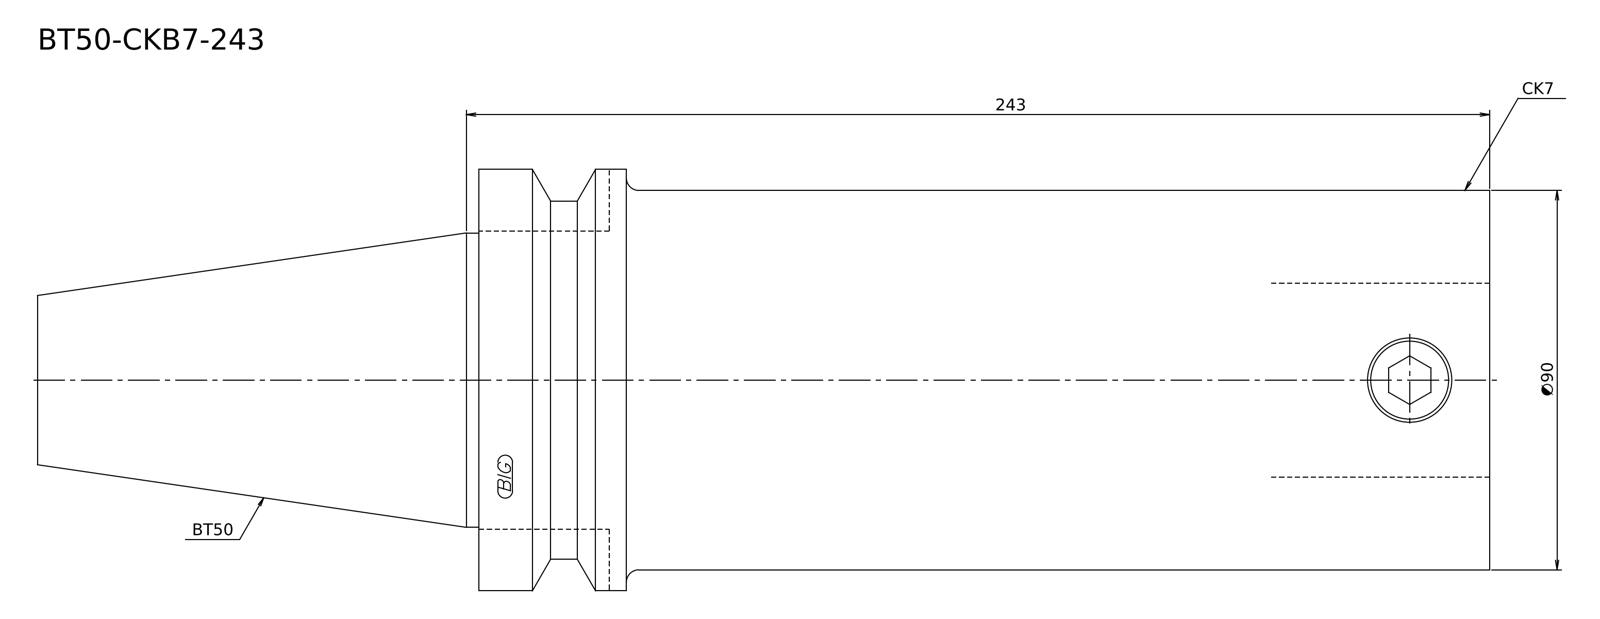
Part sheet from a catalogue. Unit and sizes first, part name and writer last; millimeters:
Units: millimetres
Overall size (bounding box): 344.8 × 100 × 100
Round bosses / shafts (diameter × count): ⌀100 ×1, ⌀90 ×1, ⌀85 ×1, ⌀69.85 ×1
Main face-to-face distances: 240, 344.8, 104.8, 205, 35, 139.8
Volume: 1 816 000 mm³ · Surface area: 102 065 mm²
Bodies: 1 solid, 13 faces (4 planar, 5 cylindrical, 4 other)
STEP written by: Kubotek KeyCreator V8.5.1 (14335) (CONFIG_CONTROL_DESIGN)
